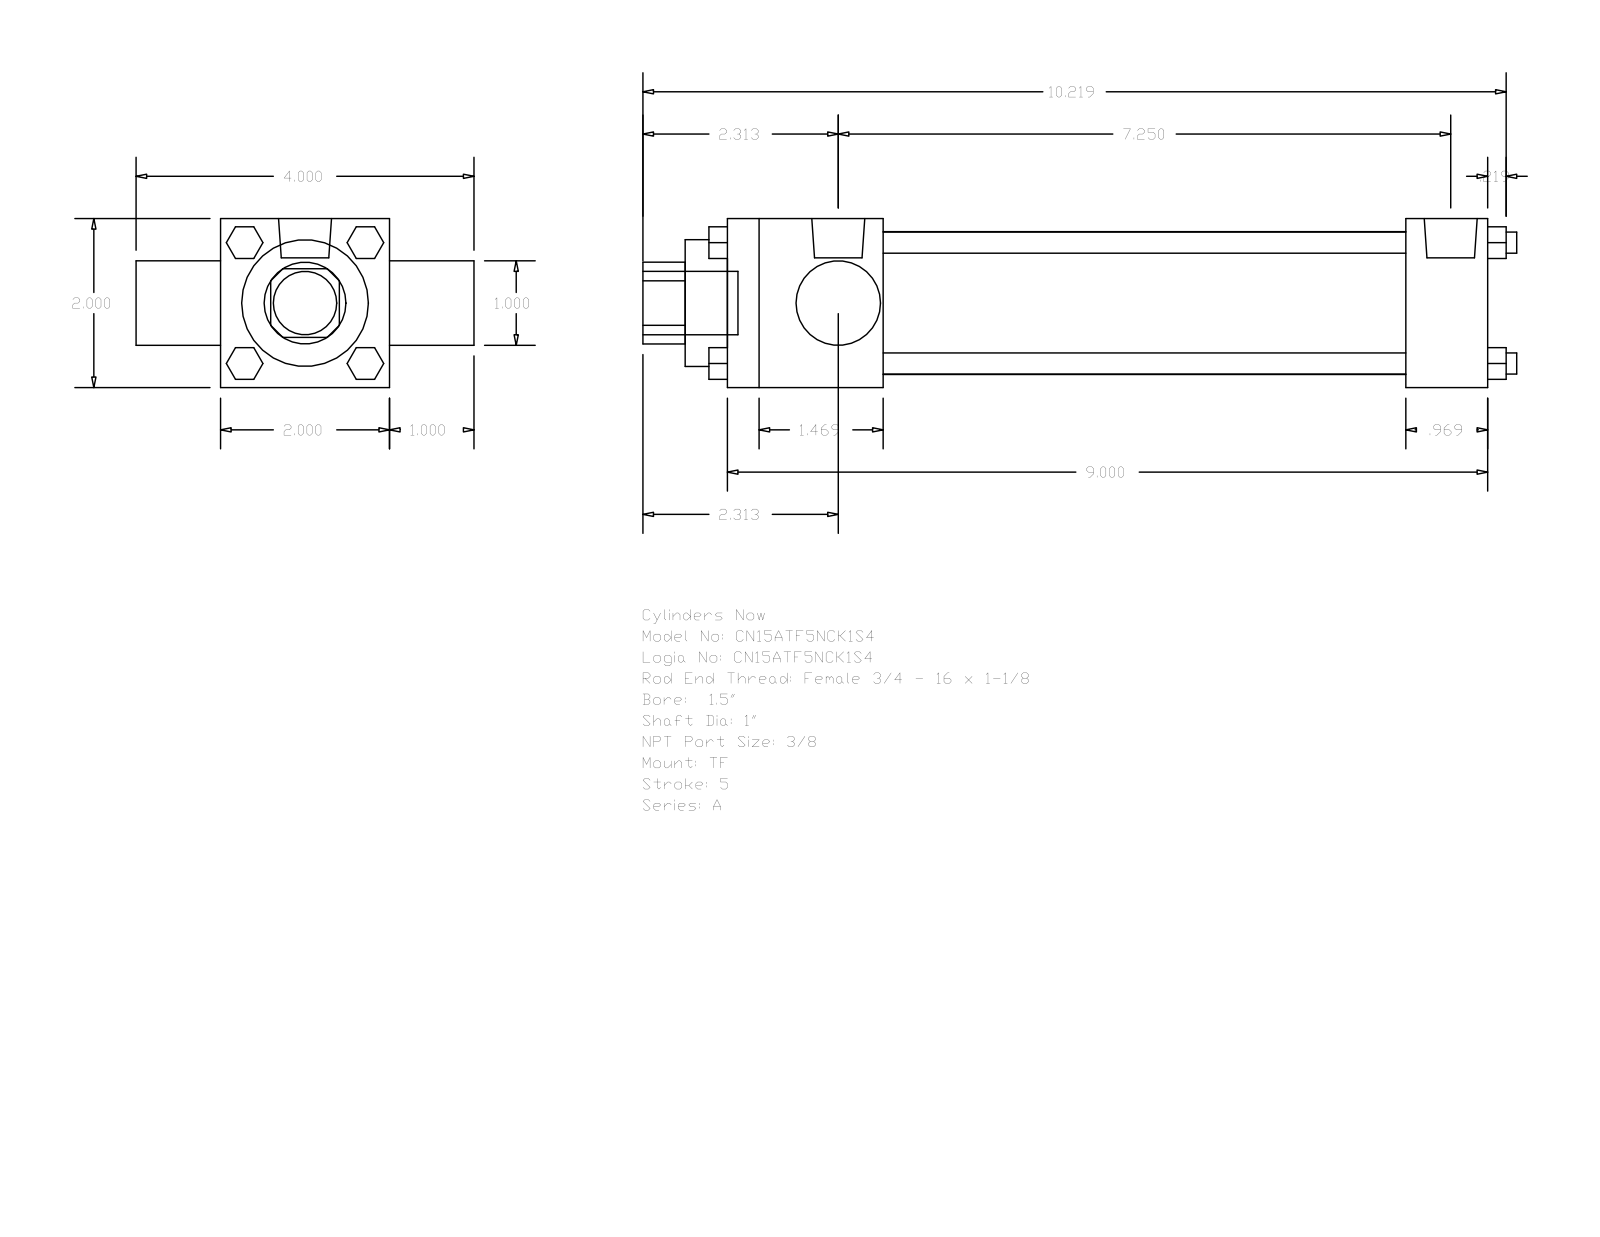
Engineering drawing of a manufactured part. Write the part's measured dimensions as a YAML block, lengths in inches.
part_name: "A_TF__0150_1"
step_written_by: "GSSL Pune (CONFIG_CONTROL_DESIGN)"
units: inches
bodies: {solids: 0, faces: 120, planar: 92, cylindrical: 28, other: 0}
overall_size: [10.344, 4, 2]
round_holes:
  - {diameter: 1, count: 2}
  - {diameter: 1.5, count: 1}
  - {diameter: 1.69, count: 1}
round_bosses_or_shafts:
  - {diameter: 0.25, count: 4}
  - {diameter: 0.219, count: 3}
  - {diameter: 0.627, count: 2}
  - {diameter: 0.75, count: 1}
partial_cylinders:
  - {radius: 0.484, count: 1}
face_to_face_distances: [2, 1, 9, 3, 1.844, 8.031, 6.187, 7.156, 0.969, 0.5]
